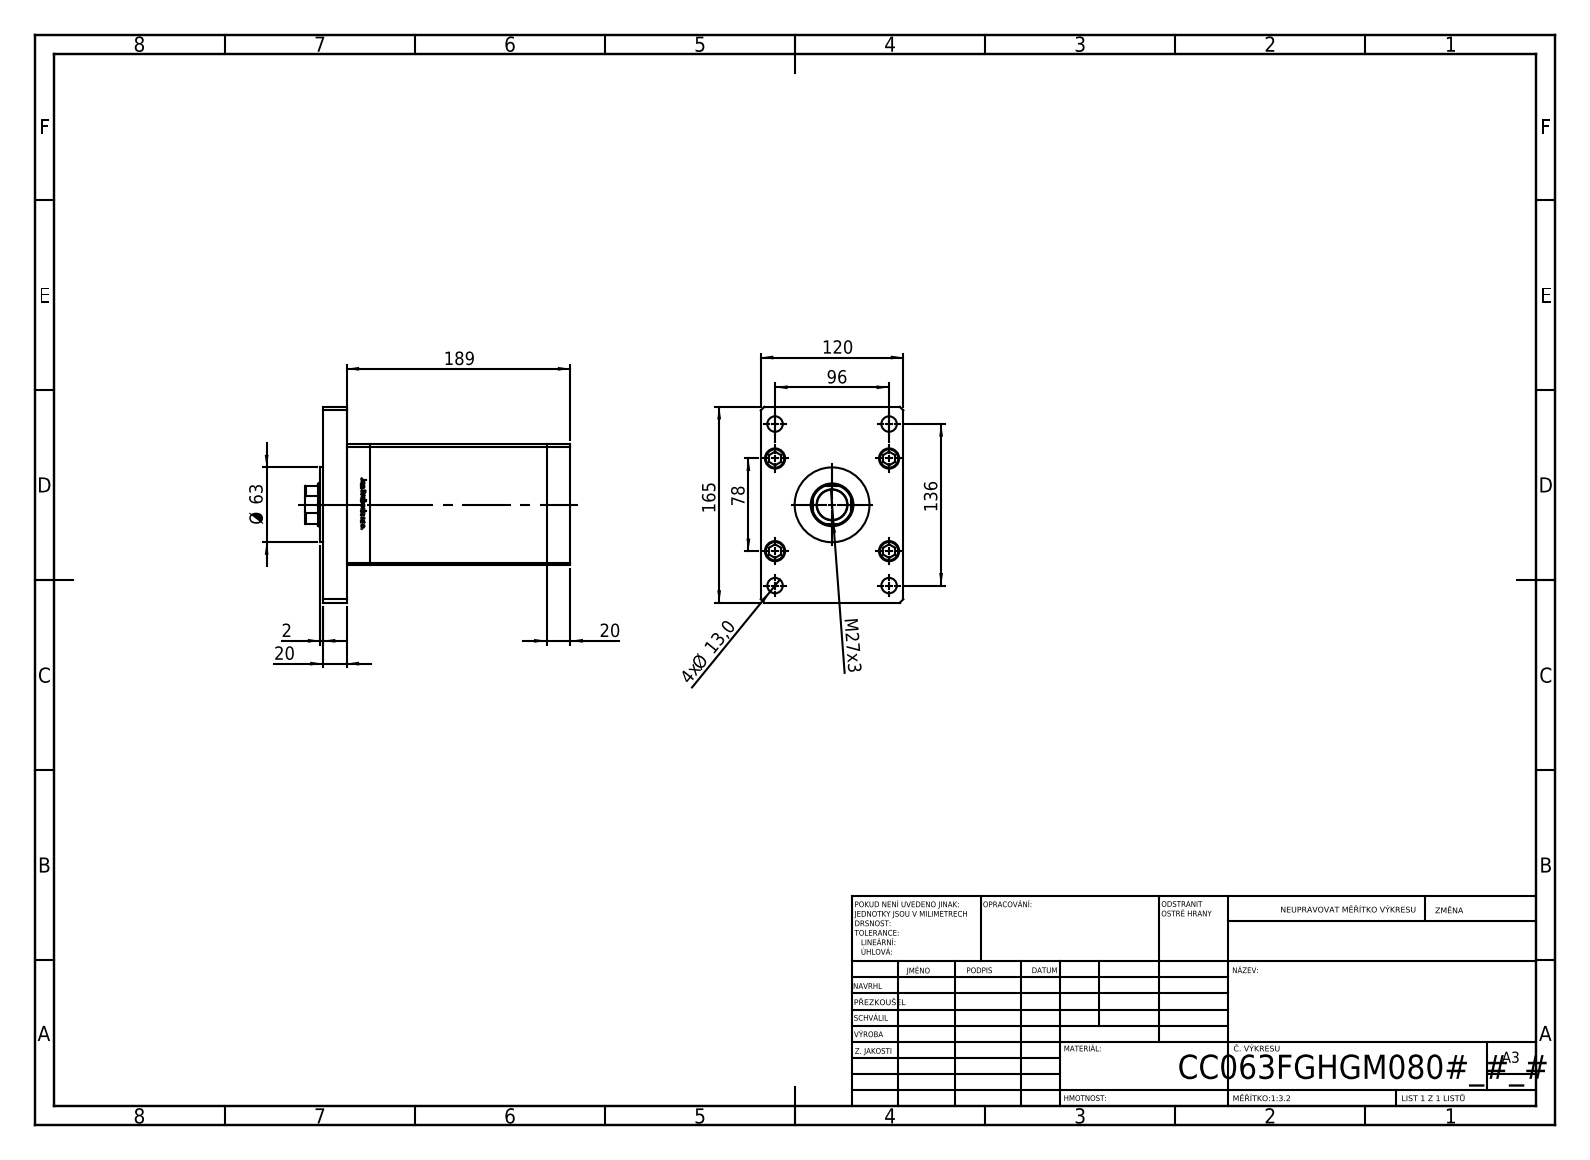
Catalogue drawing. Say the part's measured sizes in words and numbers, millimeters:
The part is named "V220C_FRONT_F; V220C BACK_F; V220C_VC_F; ALLEN BOLT (+2 more)". Its 3-D file was written by "SolidWorks 2019 (CONFIG_CONTROL_DESIGN)". It is 19 solids with 1311 faces: 517 planar, 188 cylindrical and 606 other. Overall it measures 223.5 by 165 by 120 millimeters. Its volume is 2 417 000 cubic millimeters and its surface area 321 451 square millimeters. Round holes: 5 of diameter 13.5, 5 of diameter 18, 4 of diameter 12, 4 of diameter 13, 4 of diameter 17, 2 of diameter 2, 2 of diameter 13.16, 1 of diameter 25.5, 1 of diameter 36, 1 of diameter 37.5. Round bosses or shafts: 9 of diameter 8, 5 of diameter 17, 1 of diameter 63. Partial cylindrical surfaces (rounded edges, fillets, slot ends): 2 of radius 0.93, 1 of radius 17.5. The main face-to-face distances are 20, 168.5, 188.5, 120, 102, 148.5, 40, 208.5, 34.25, 42. The hole center spacings are 41.5, 29, 61.85, 83.23, 96, 100.28, 107, 143.75.
